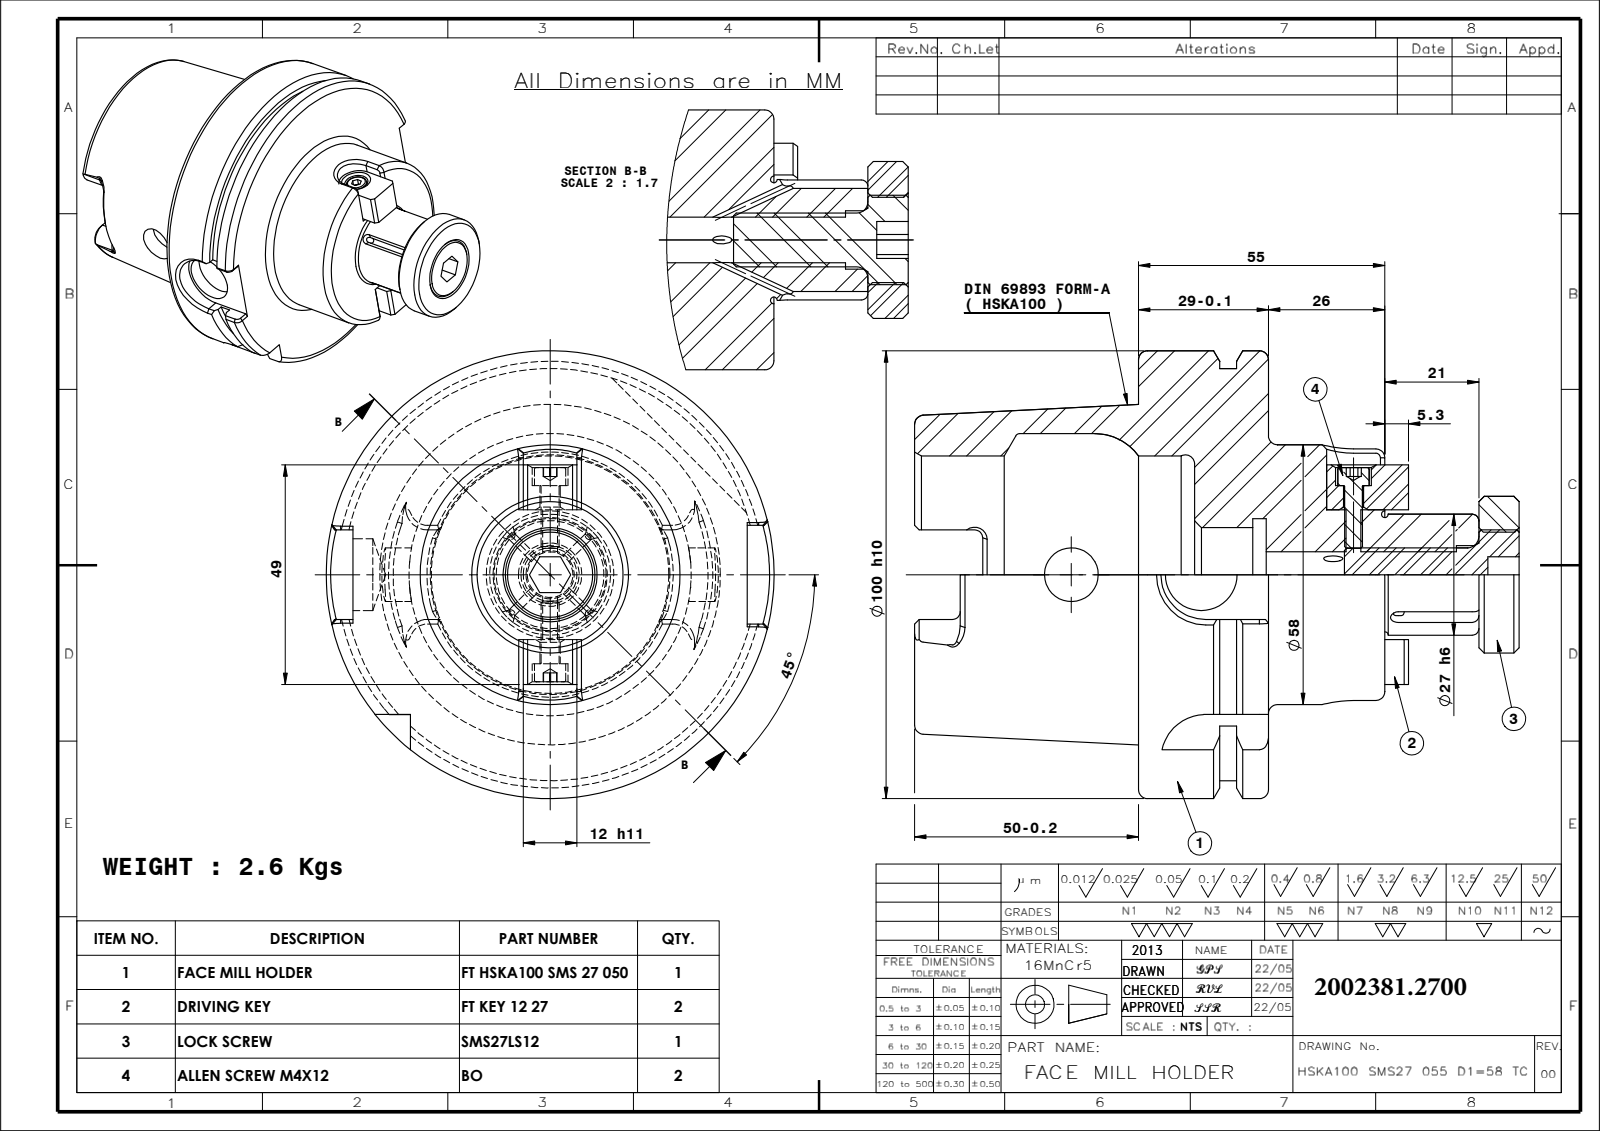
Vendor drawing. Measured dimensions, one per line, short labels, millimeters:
name: SMS27LS12-2; M4X12_DIN 912 M4 x 10 --- 10N; FT KEY 12 27; HSKA100 SMS27 055 D1=58 TC (+2 more)
written by: SolidWorks 2009 (CONFIG_CONTROL_DESIGN)
unit: mm
bodies: 7 solids, 354 faces (134 planar, 94 cylindrical, 126 other)
size: 135 × 100 × 100
volume: 340 780 mm³; area: 66 514 mm²
holes: 4× ⌀1.8, 1× ⌀3.3, 1× ⌀4.5, 1× ⌀8, 1× ⌀10.2, 1× ⌀12, 1× ⌀13, 1× ⌀16, 1× ⌀19, 1× ⌀21, 1× ⌀25, 1× ⌀53
bosses: 1× ⌀100, 1× ⌀92, 1× ⌀58, 1× ⌀35, 1× ⌀27, 1× ⌀20, 1× ⌀12, 1× ⌀7
rounds: 6× R1.8, 4× R1, 4× R4.88, 2× R10, 1× R6, 1× R11
face distances: 29, 50, 12.5, 16.5, 42.5, 55, 26, 21, 62.5, 79
hole spacings: 29
